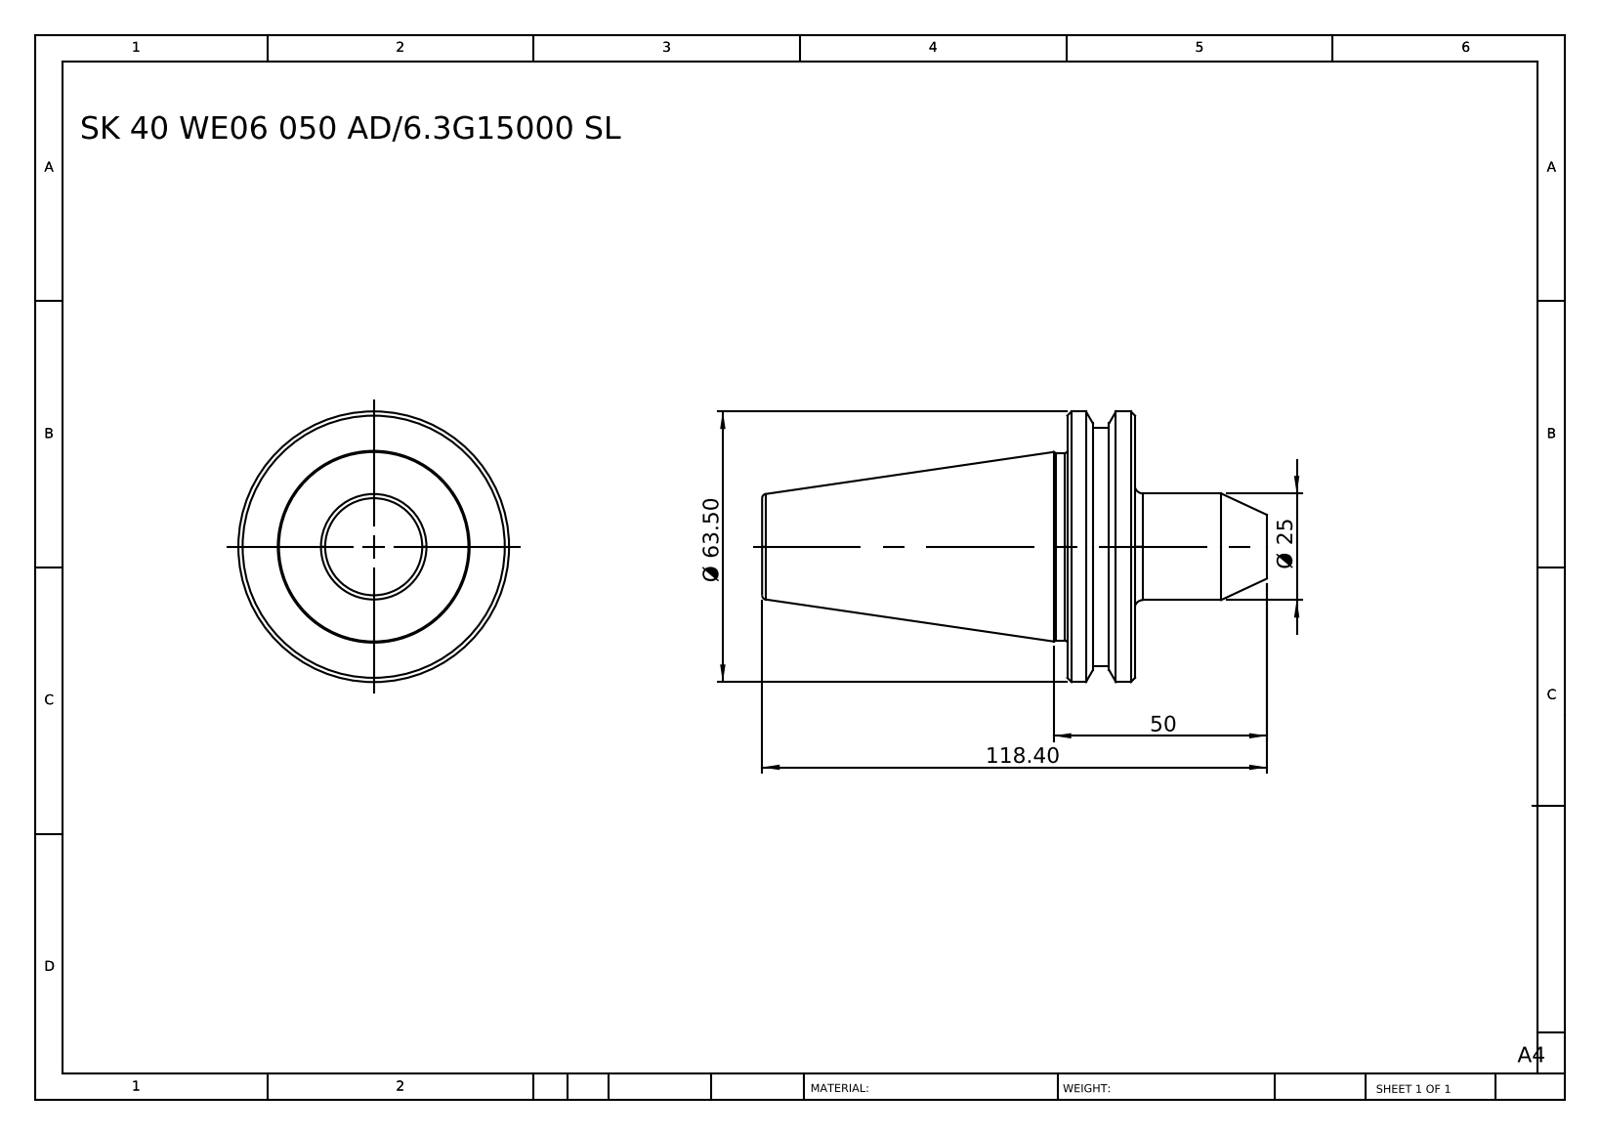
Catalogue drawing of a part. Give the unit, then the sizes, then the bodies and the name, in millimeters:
Units: millimetres
Overall size (bounding box): 118.4 × 63.5 × 63.5
Round bosses / shafts (diameter × count): ⌀63.5 ×1, ⌀56 ×1, ⌀44 ×1, ⌀25 ×1
Main face-to-face distances: 15.9, 87.5, 71.6, 30.9, 46.8, 118.4, 40.8, 9.9, 6, 77.6
Volume: 130 498 mm³ · Surface area: 18 896 mm²
Bodies: 1 solid, 36 faces (6 planar, 10 cylindrical, 20 other)
Part name (STEP PRODUCT): SK40 WE06 050 AD-6.3G15000 SL
STEP written by: SolidWorks 2014 (CONFIG_CONTROL_DESIGN)
